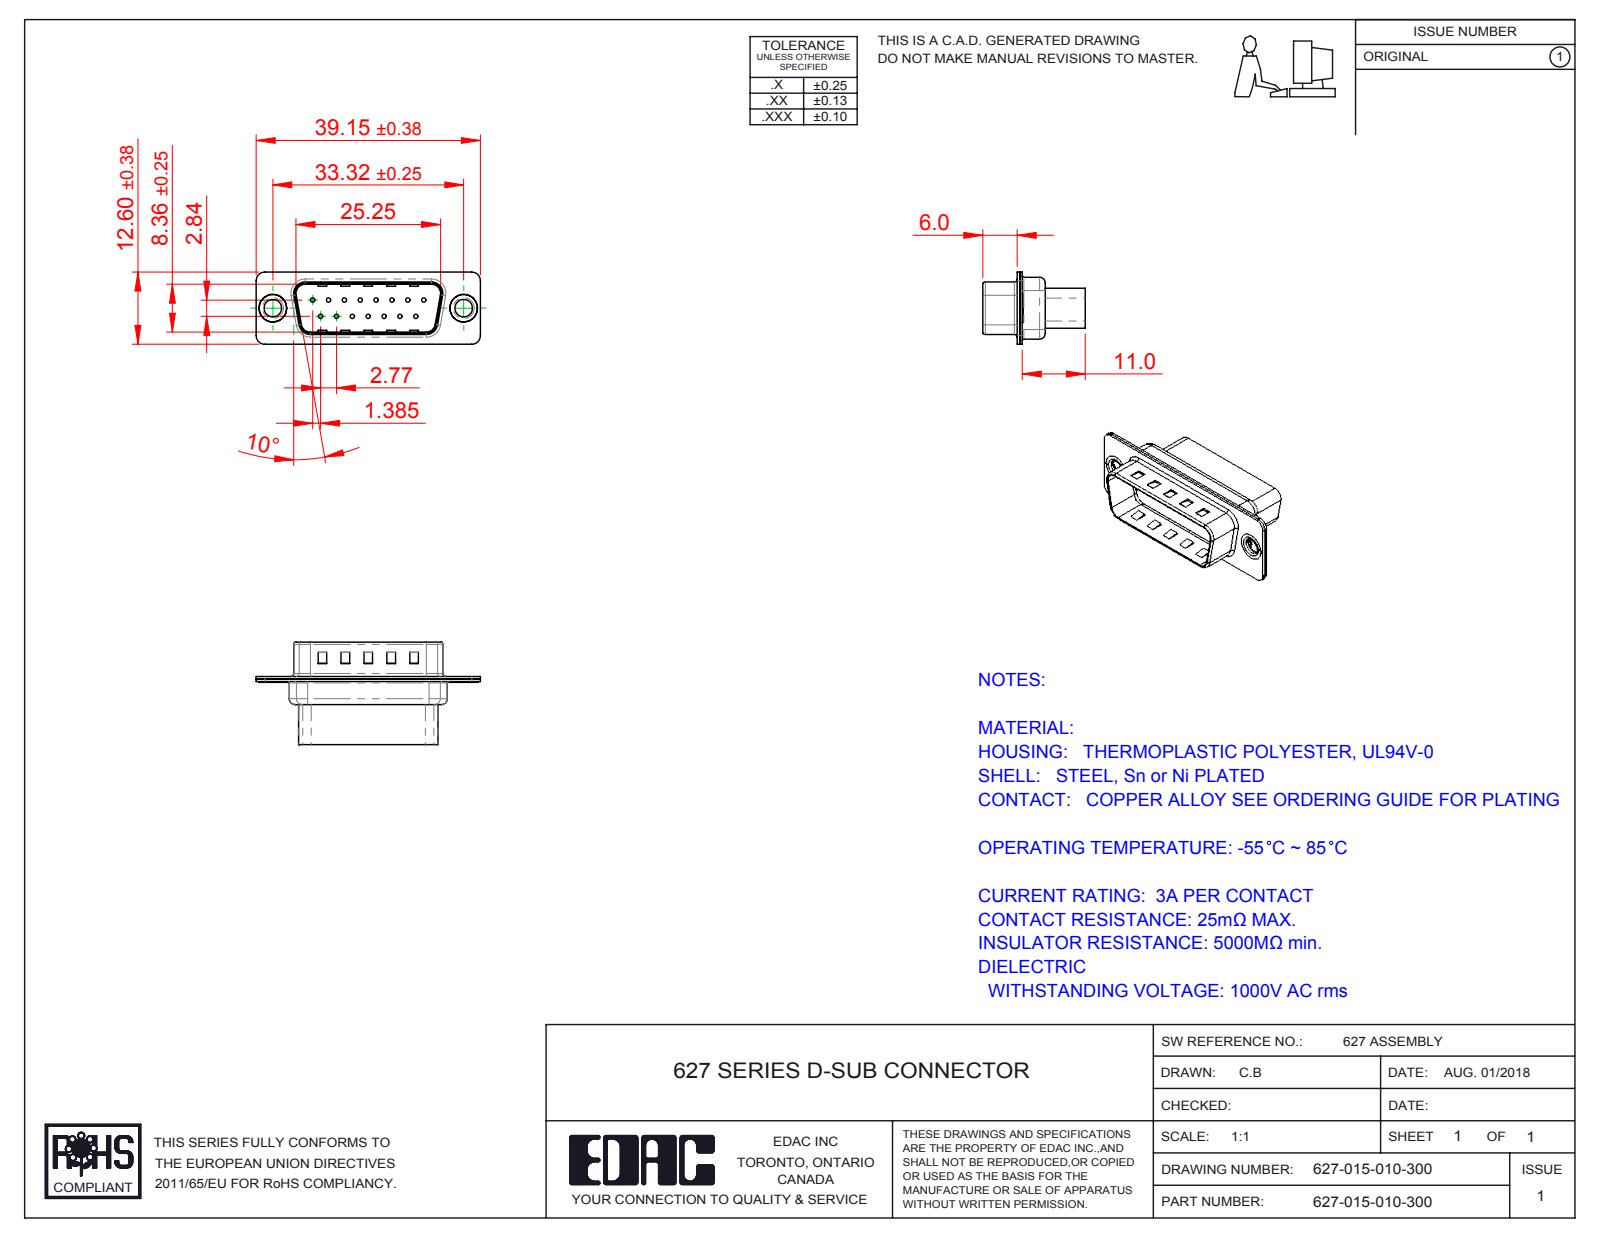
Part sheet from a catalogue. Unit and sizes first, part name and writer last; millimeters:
Units: millimetres
Overall size (bounding box): 39.15 × 17.9 × 12.6
Round holes (diameter × count): ⌀0.75 ×15, ⌀1.6 ×15, ⌀2 ×15, ⌀3.05 ×2, ⌀4 ×2, ⌀4.8 ×2
Round bosses / shafts (diameter × count): ⌀5 ×2, ⌀4.9 ×2, ⌀3.55 ×2
Partial cylindrical surfaces — rounded edges, fillets, slot ends (radius × count): R1.5 ×16, R2 ×12, R0.5 ×8, R1.6 ×8, R0.25 ×4, R0.6 ×4, R0.65 ×4, R0.9 ×4
Main face-to-face distances: 0.4, 0.45, 0.9, 0.82, 9.58, 0.68, 7.68, 1.08, 8.08, 8.76
Hole centre spacings: 3.16, 2.77, 5.54, 8.31, 11.08, 5.03, 5.04, 7.48
Volume: 2 353 mm³ · Surface area: 4 638 mm²
Bodies: 5 solids, 434 faces (169 planar, 207 cylindrical, 58 other)
Part name (STEP PRODUCT): 627 Shell Front_15 Contacts; 627-015-010-300; 627 Housing_15 HP; 627 Shell Rear_15 Contacts (+1 more)
STEP written by: SolidWorks 2016 (CONFIG_CONTROL_DESIGN)
